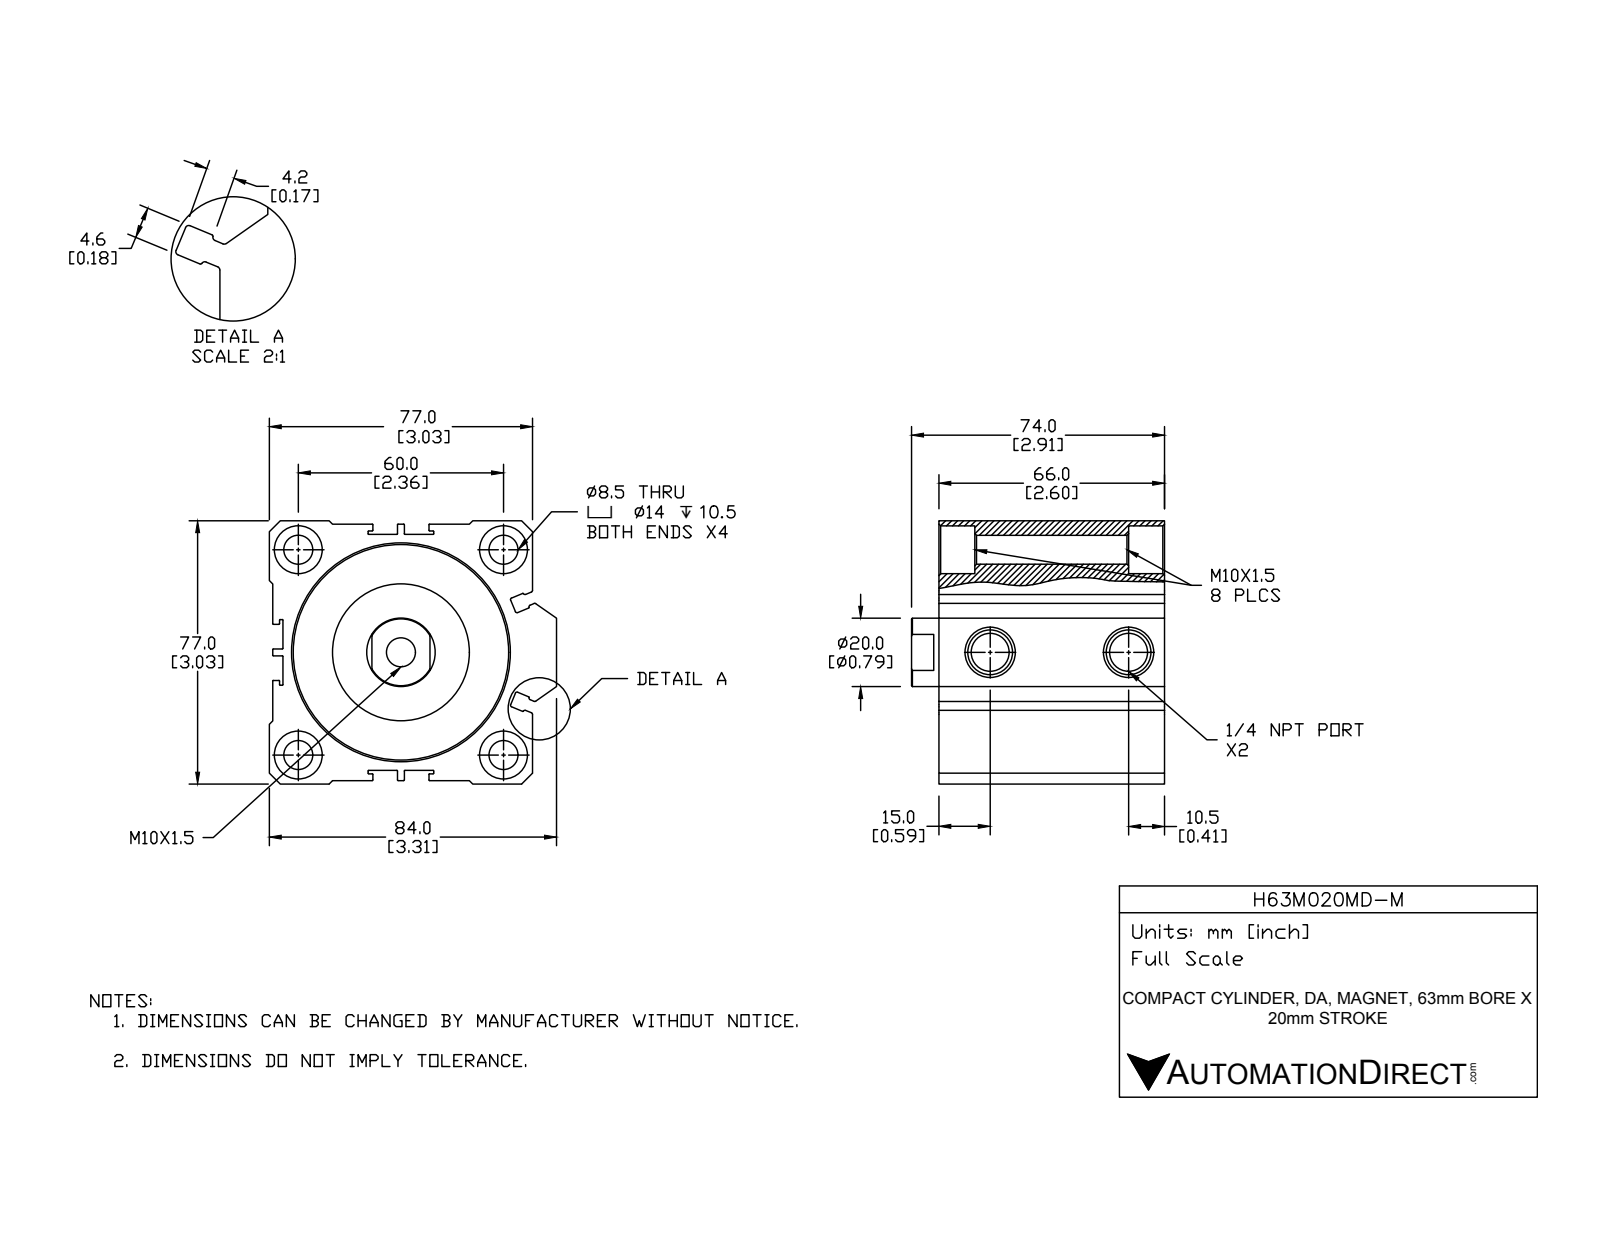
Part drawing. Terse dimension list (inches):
name: H63M020MD-M-PISTON; H63M020MD-M; H63M020MD-M-BODY
written by: SolidWorks 2015 (CONFIG_CONTROL_DESIGN)
unit: in
bodies: 2 solids, 255 faces (99 planar, 103 cylindrical, 53 other)
size: 3.307 × 3.031 × 2.913
volume: 17.16 in³; area: 119.7 in²
holes: 5× ⌀0.335, 4× ⌀0.551, 2× ⌀0.438, 1× ⌀0.787, 1× ⌀1.792, 1× ⌀2.48
bosses: 1× ⌀1.575, 1× ⌀1.535
rounds: 40× R0.008, 12× R0.02
face distances: 0.039, 2.992, 0.118, 3.031, 0.157, 2.874, 0.906, 1.713, 0.807, 0.079
hole spacings: 1.67, 2.362, 3.341, 1.594
